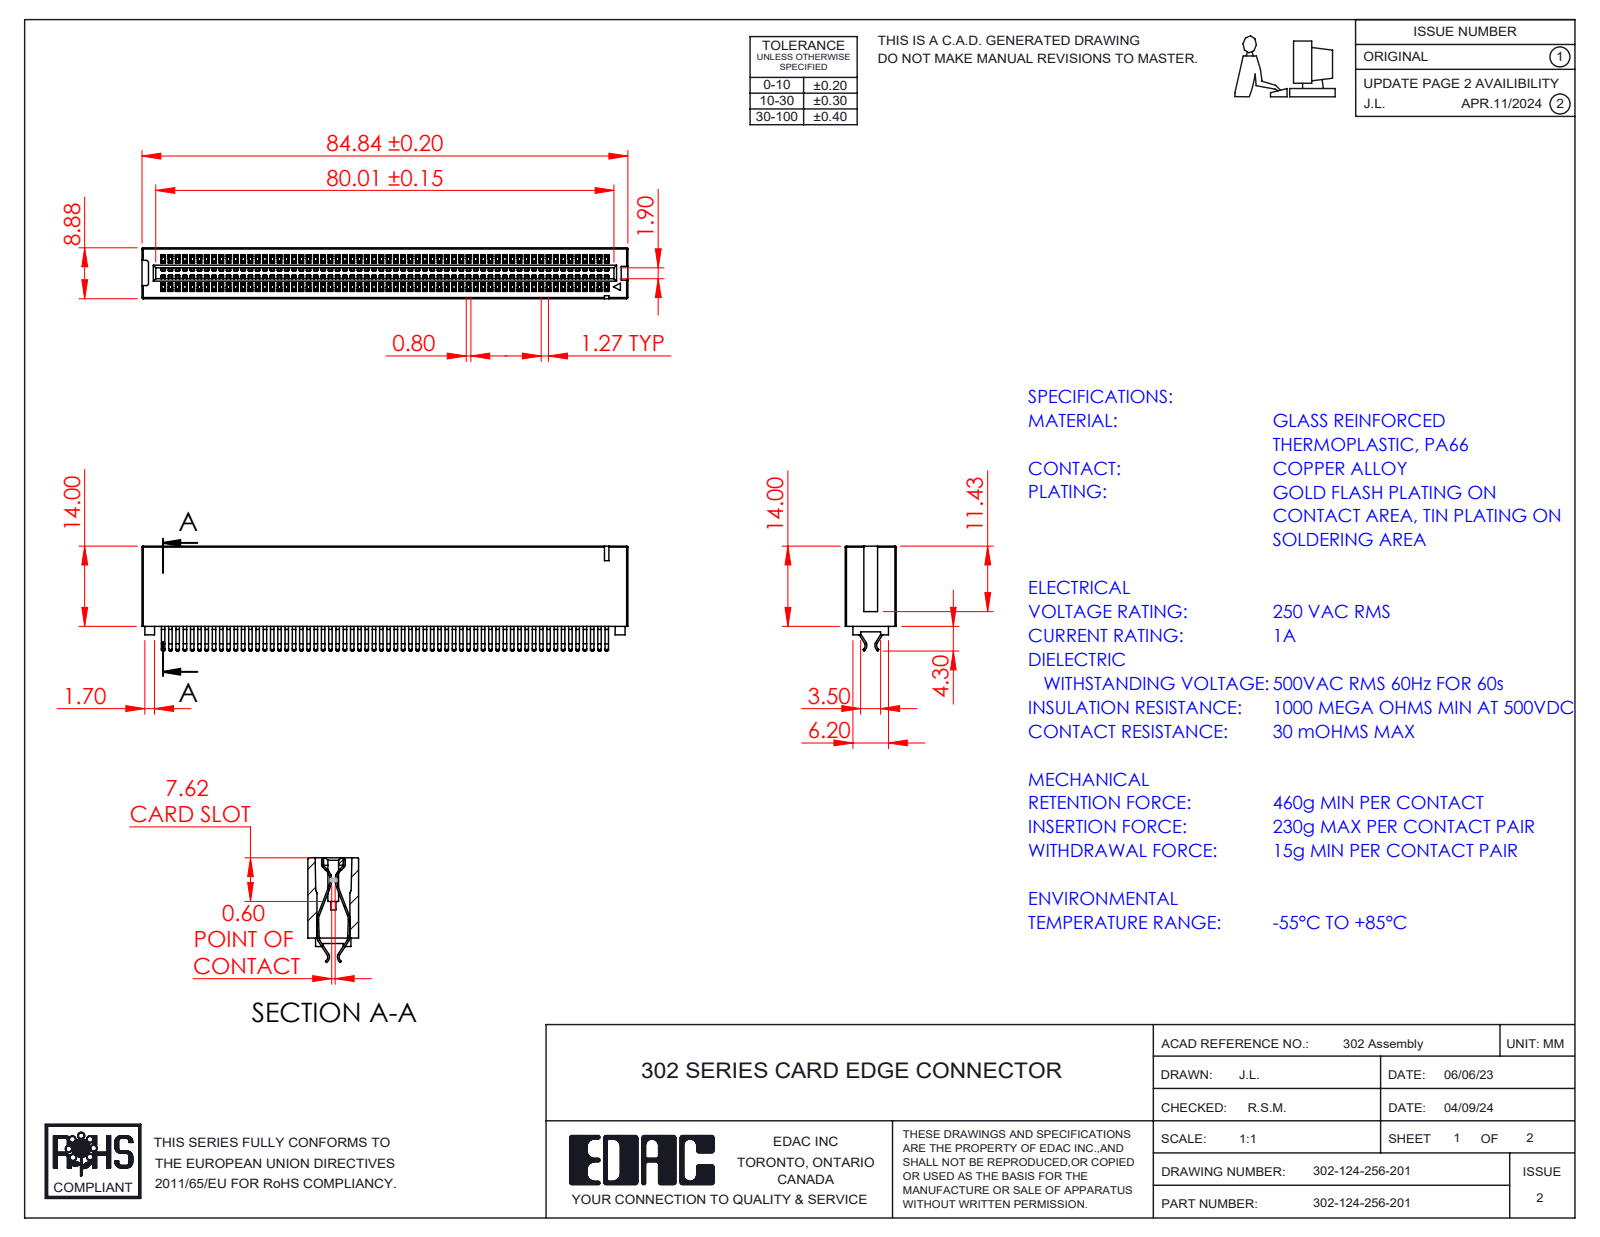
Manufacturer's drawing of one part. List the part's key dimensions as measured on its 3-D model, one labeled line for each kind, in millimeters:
Part name (STEP PRODUCT): Contact_302-290-X56; 302-124-256-201; HSG_Vertical HSG
STEP written by: SolidWorks 2023 (CONFIG_CONTROL_DESIGN)
Units: millimetres
Bodies: 125 solids, 5956 faces (3955 planar, 1997 cylindrical, 4 other)
Overall size (bounding box): 84.84 × 18.3 × 8.88
Volume: 6 461 mm³ · Surface area: 18 717 mm²
Partial cylindrical surfaces — rounded edges, fillets, slot ends (radius × count): R0.2 ×380, R0.11 ×2, R0.4 ×2, R0.41 ×2, R0.93 ×2, R1.05 ×2, R1.23 ×2, R1.25 ×2
Main face-to-face distances: 8.88, 1.27, 2.54, 3.81, 0.8, 0.47, 1.9, 5.08, 3.49, 5.39
